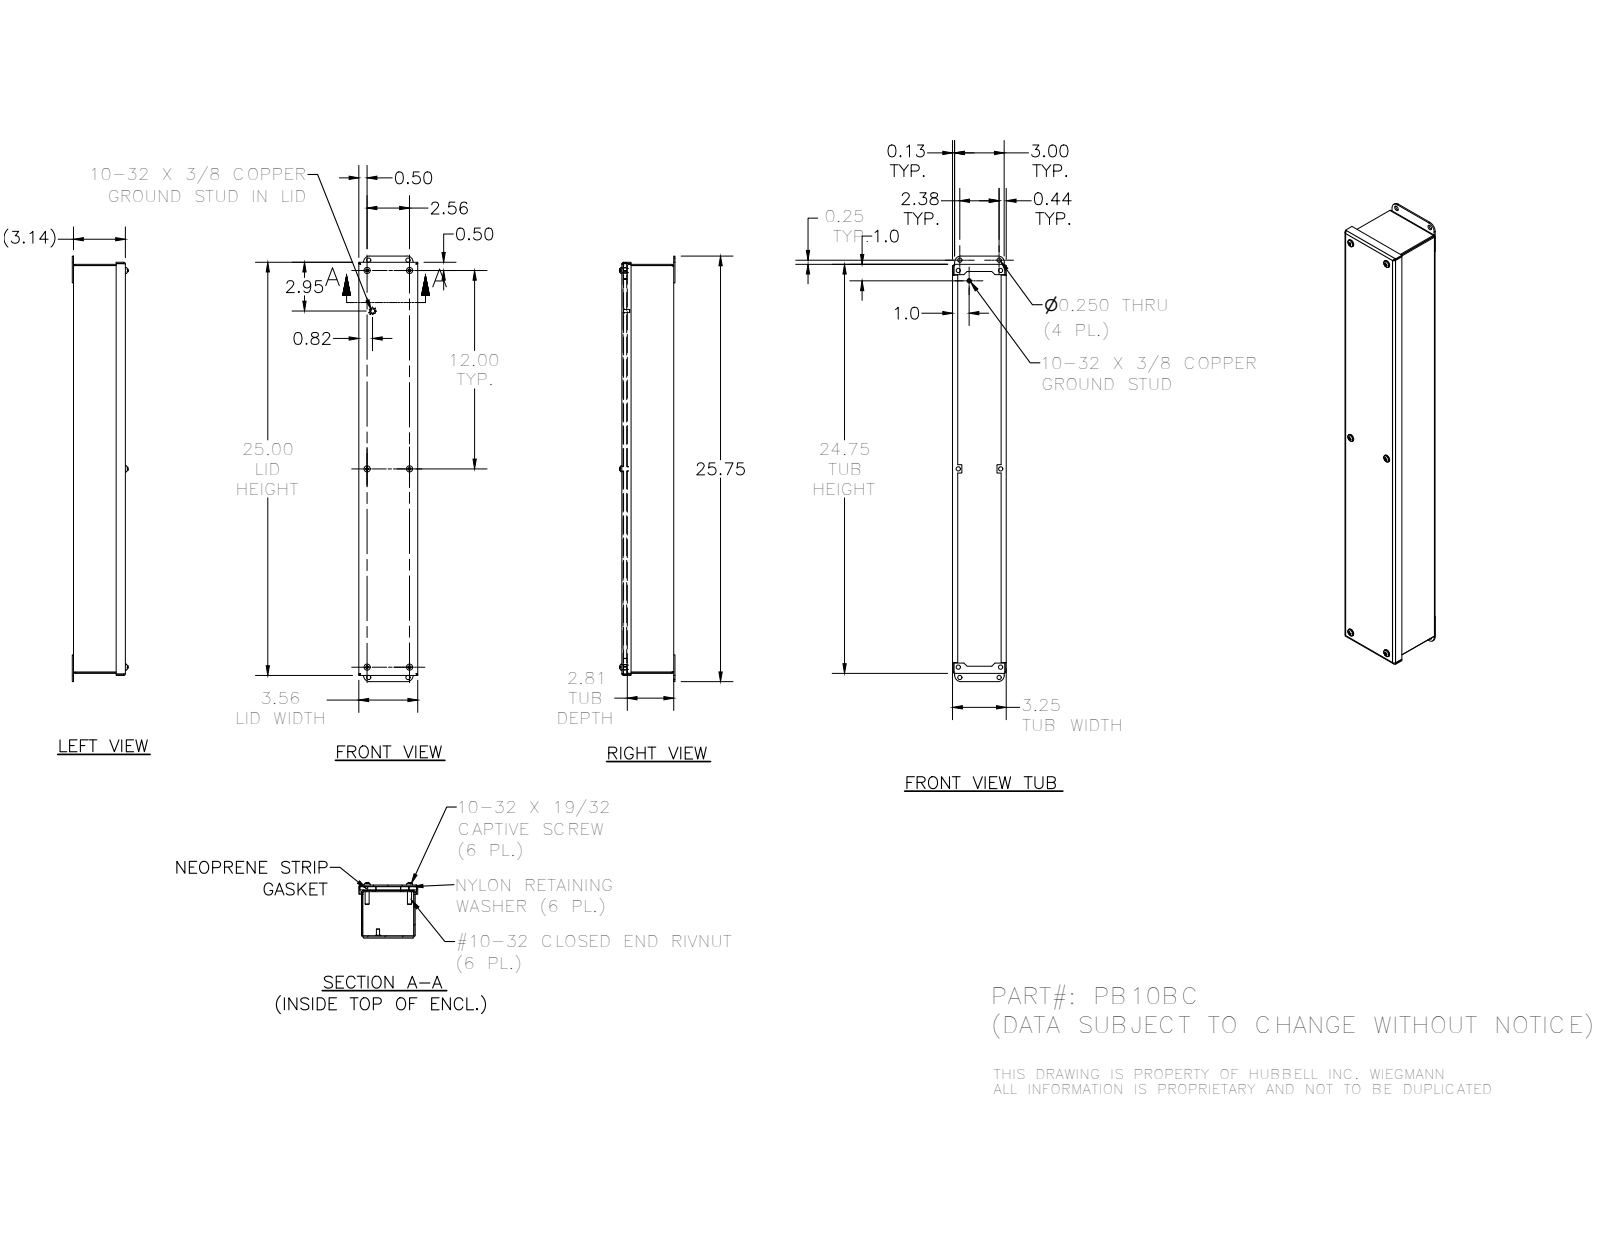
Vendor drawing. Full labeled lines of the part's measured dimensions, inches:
Part name (STEP PRODUCT): 39077; PB_corner gasket; 22.75; 1.25 (+7 more)
STEP written by: Autodesk Inventor 2016 (AUTOMOTIVE_DESIGN)
Units: inches
Bodies: 32 solids, 668 faces (386 planar, 124 cylindrical, 158 other)
Overall size (bounding box): 25.75 × 3.563 × 3.346
Volume: 32.71 in³ · Surface area: 838.5 in²
Round holes (diameter × count): ⌀0.156 ×6, ⌀0.196 ×6, ⌀0.278 ×6, ⌀0.281 ×6, ⌀0.257 ×5, ⌀0.25 ×4, ⌀0.313 ×4, ⌀0.257 ×1
Round bosses / shafts (diameter × count): ⌀0.19 ×8, ⌀0.453 ×6, ⌀0.406 ×6, ⌀0.373 ×6, ⌀0.248 ×6, ⌀0.25 ×2
Partial cylindrical surfaces — rounded edges, fillets, slot ends (radius × count): R0.031 ×12, R0.105 ×12, R0.089 ×6, R0.375 ×4
Main face-to-face distances: 0.074, 3.068, 3.176, 3.142, 2.994, 3.25, 3.102, 0.106, 0.032, 2.962
Hole centre spacings: 12, 24, 24.136, 12.27, 24.009, 24.625, 24.748, 0.632
